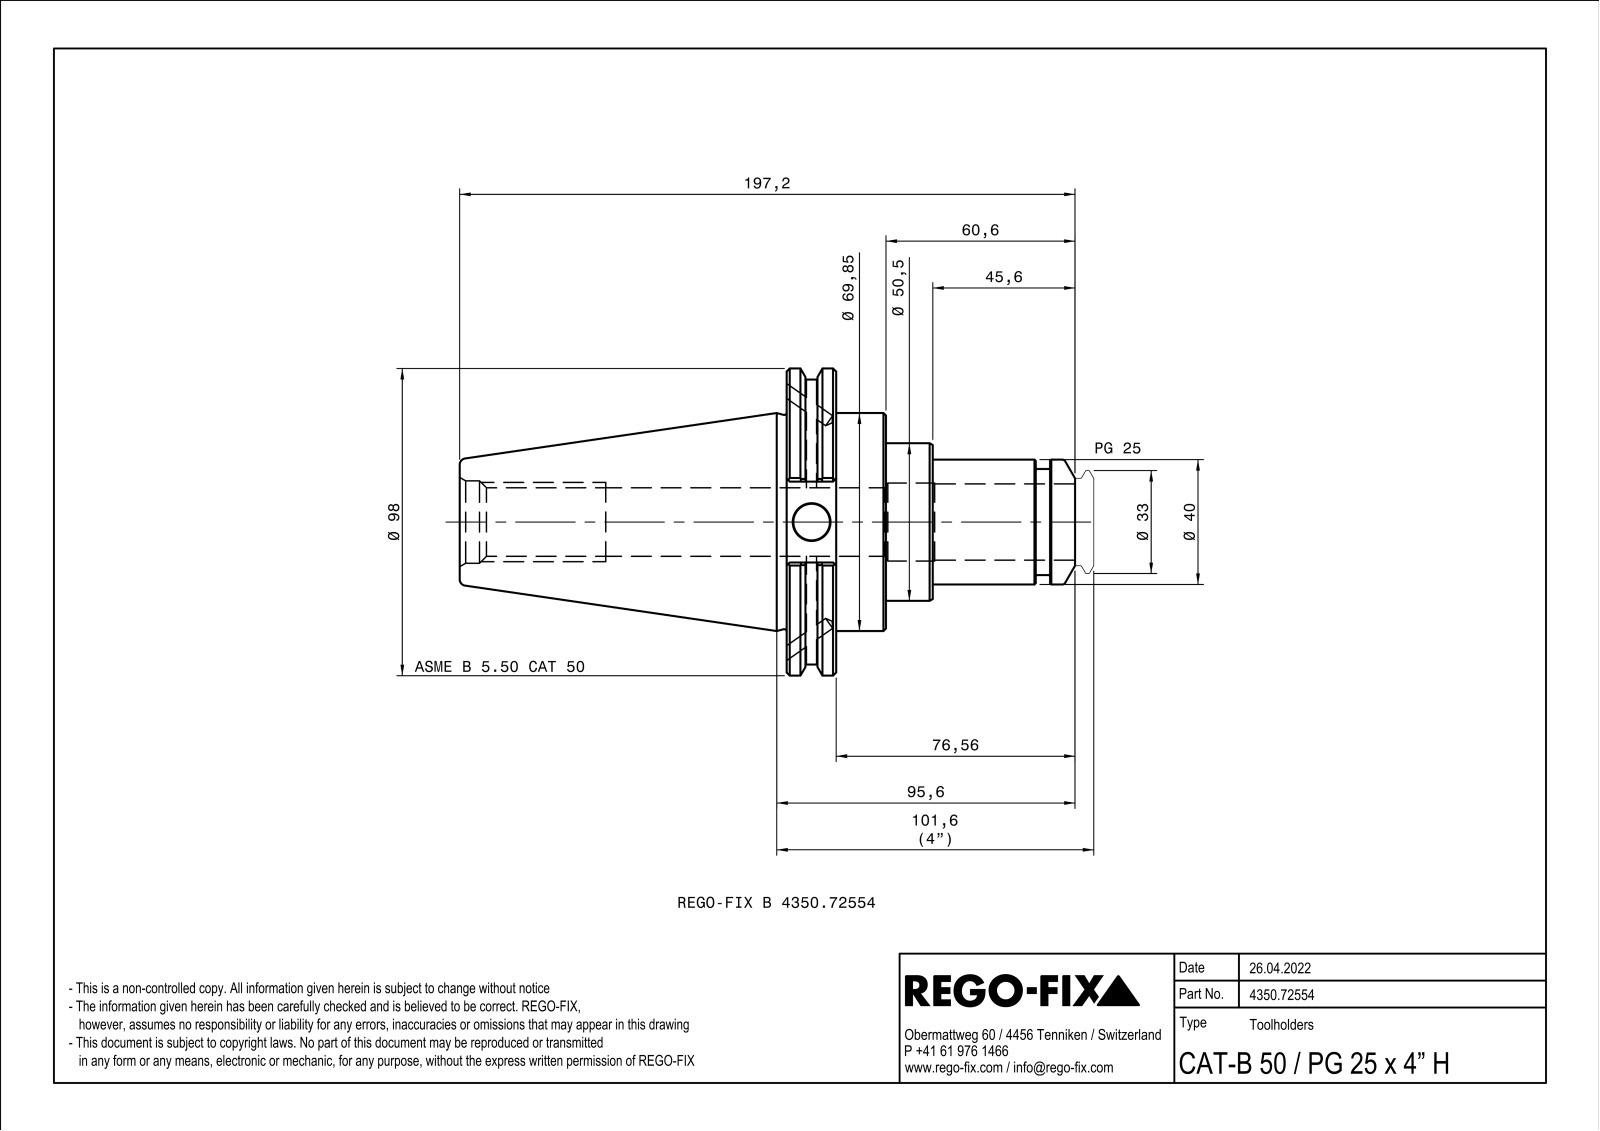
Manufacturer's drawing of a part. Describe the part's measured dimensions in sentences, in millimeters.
The part is named "NOCUT". Its 3-D file was written by "SIEMENS PLM Software Solid Edge ST10 (AUTOMOTIVE_DESIGN)". It is 1 solid with 117 faces: 35 planar, 31 cylindrical and 51 other. Overall it measures 197.2 by 98.42 by 94.39 millimeters. Its volume is 427 234 cubic millimeters and its surface area 61 153 square millimeters. Round holes: 1 of diameter 11.7, 1 of diameter 21.96, 1 of diameter 25, 1 of diameter 26.4. Round bosses or shafts: 1 of diameter 98.42, 1 of diameter 91.3, 1 of diameter 69.85, 1 of diameter 50.5, 1 of diameter 40, 1 of diameter 34. Partial cylindrical surfaces (rounded edges, fillets, slot ends): 12 of radius 0.5. The main face-to-face distances are 15.87, 15.96, 31.83, 136.6, 120.64, 104.77, 15, 30.96, 46.83, 151.6.
